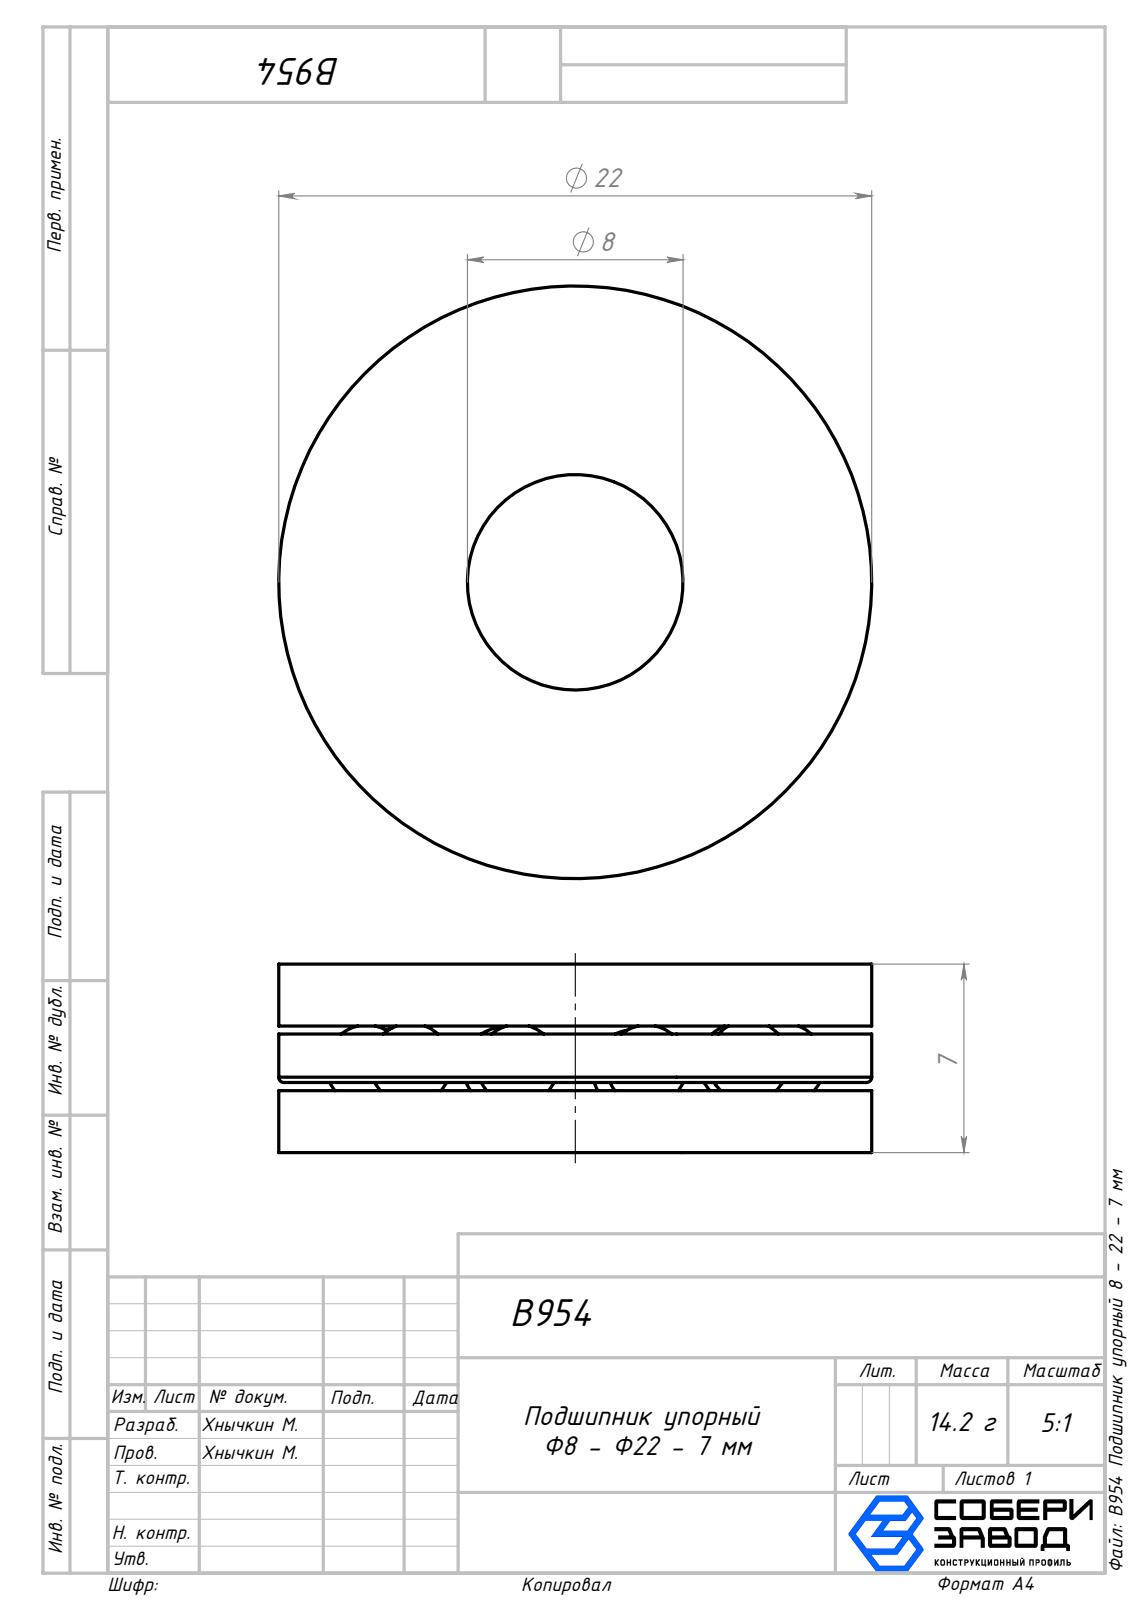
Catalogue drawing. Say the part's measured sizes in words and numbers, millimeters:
The part is named "B954 Подшипник упорный 8 - 22 - 7 мм; B954 Шарик_00; B954 Первая часть_00; B954 Внутренняя часть_00". Its 3-D file was written by "SolidWorks 2026 (AUTOMOTIVE_DESIGN)". It is 13 solids with 86 faces: 12 planar, 44 cylindrical and 30 other. Overall it measures 22 by 22 by 7 millimeters. Its volume is 1 788 cubic millimeters and its surface area 2 961 square millimeters. Round holes: 10 of diameter 3, 1 of diameter 8, 1 of diameter 9, 1 of diameter 16.8, 1 of diameter 21.6. Round bosses or shafts: 1 of diameter 22, 1 of diameter 13.2, 1 of diameter 9.4. The main face-to-face distances are 2.3, 4.7, 3.5, 1.2, 7, 2.6, 4.4, 2.1, 0.9, 2.4. The hole center spacings are 12.54, 4.79, 7.75, 9.11, 14.74, 14.75, 15.5, 4.8.
